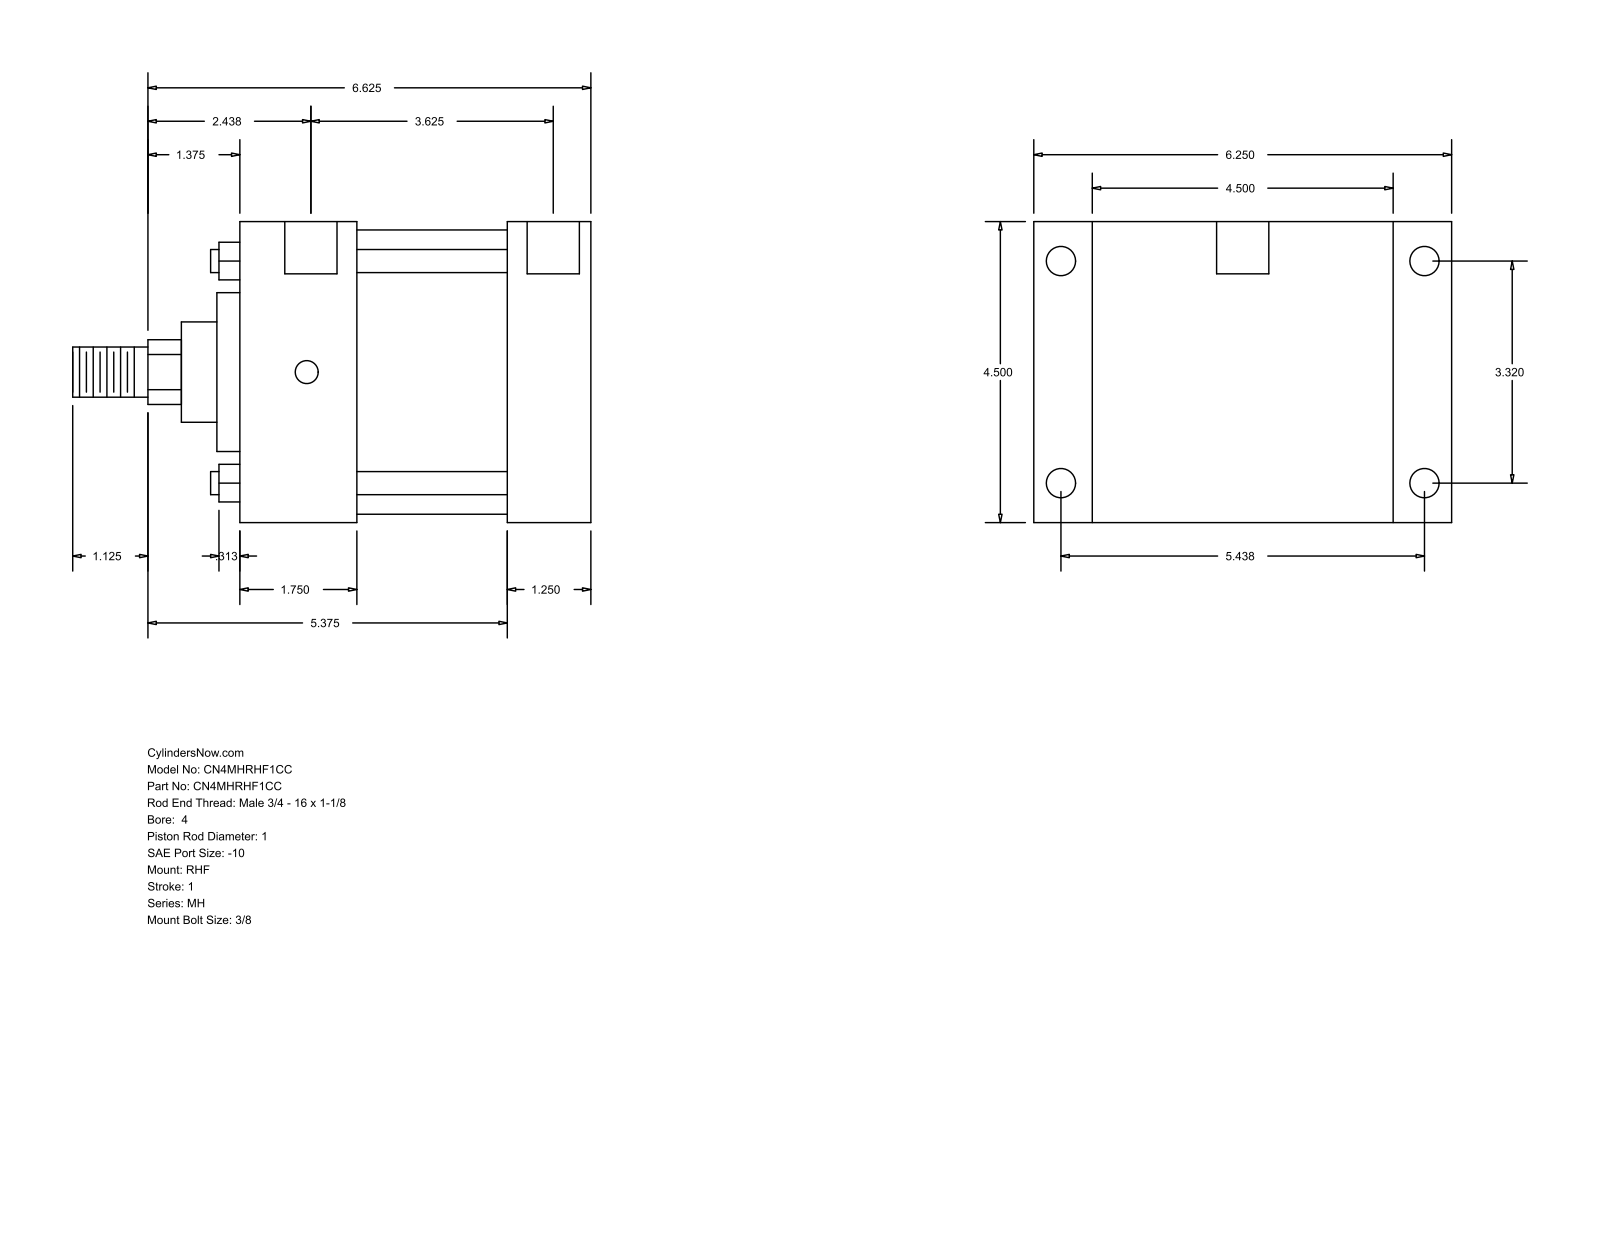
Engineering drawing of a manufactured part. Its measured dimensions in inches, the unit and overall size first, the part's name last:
Units: inches
Overall size (bounding box): 7.75 × 6.25 × 4.5
Round holes (diameter × count): ⌀0.344 ×4, ⌀0.438 ×4, ⌀0.781 ×2
Round bosses / shafts (diameter × count): ⌀0.345 ×4, ⌀4.25 ×1, ⌀2.375 ×1, ⌀1.5 ×1, ⌀1 ×1, ⌀0.75 ×1
Partial cylindrical surfaces — rounded edges, fillets, slot ends (radius × count): R0.484 ×1
Main face-to-face distances: 4.5, 5.25, 4, 1.25, 5.375, 0.875, 1.75, 2.25, 3.5, 6.25
Hole centre spacings: 0.062, 3.32, 3.687, 3.75, 5.438, 6.371, 3.625
Bodies: 0 solids, 90 faces (61 planar, 29 cylindrical, 0 other)
Part name (STEP PRODUCT): MH_RHF__0400_1
STEP written by: GSSL Pune (CONFIG_CONTROL_DESIGN)
